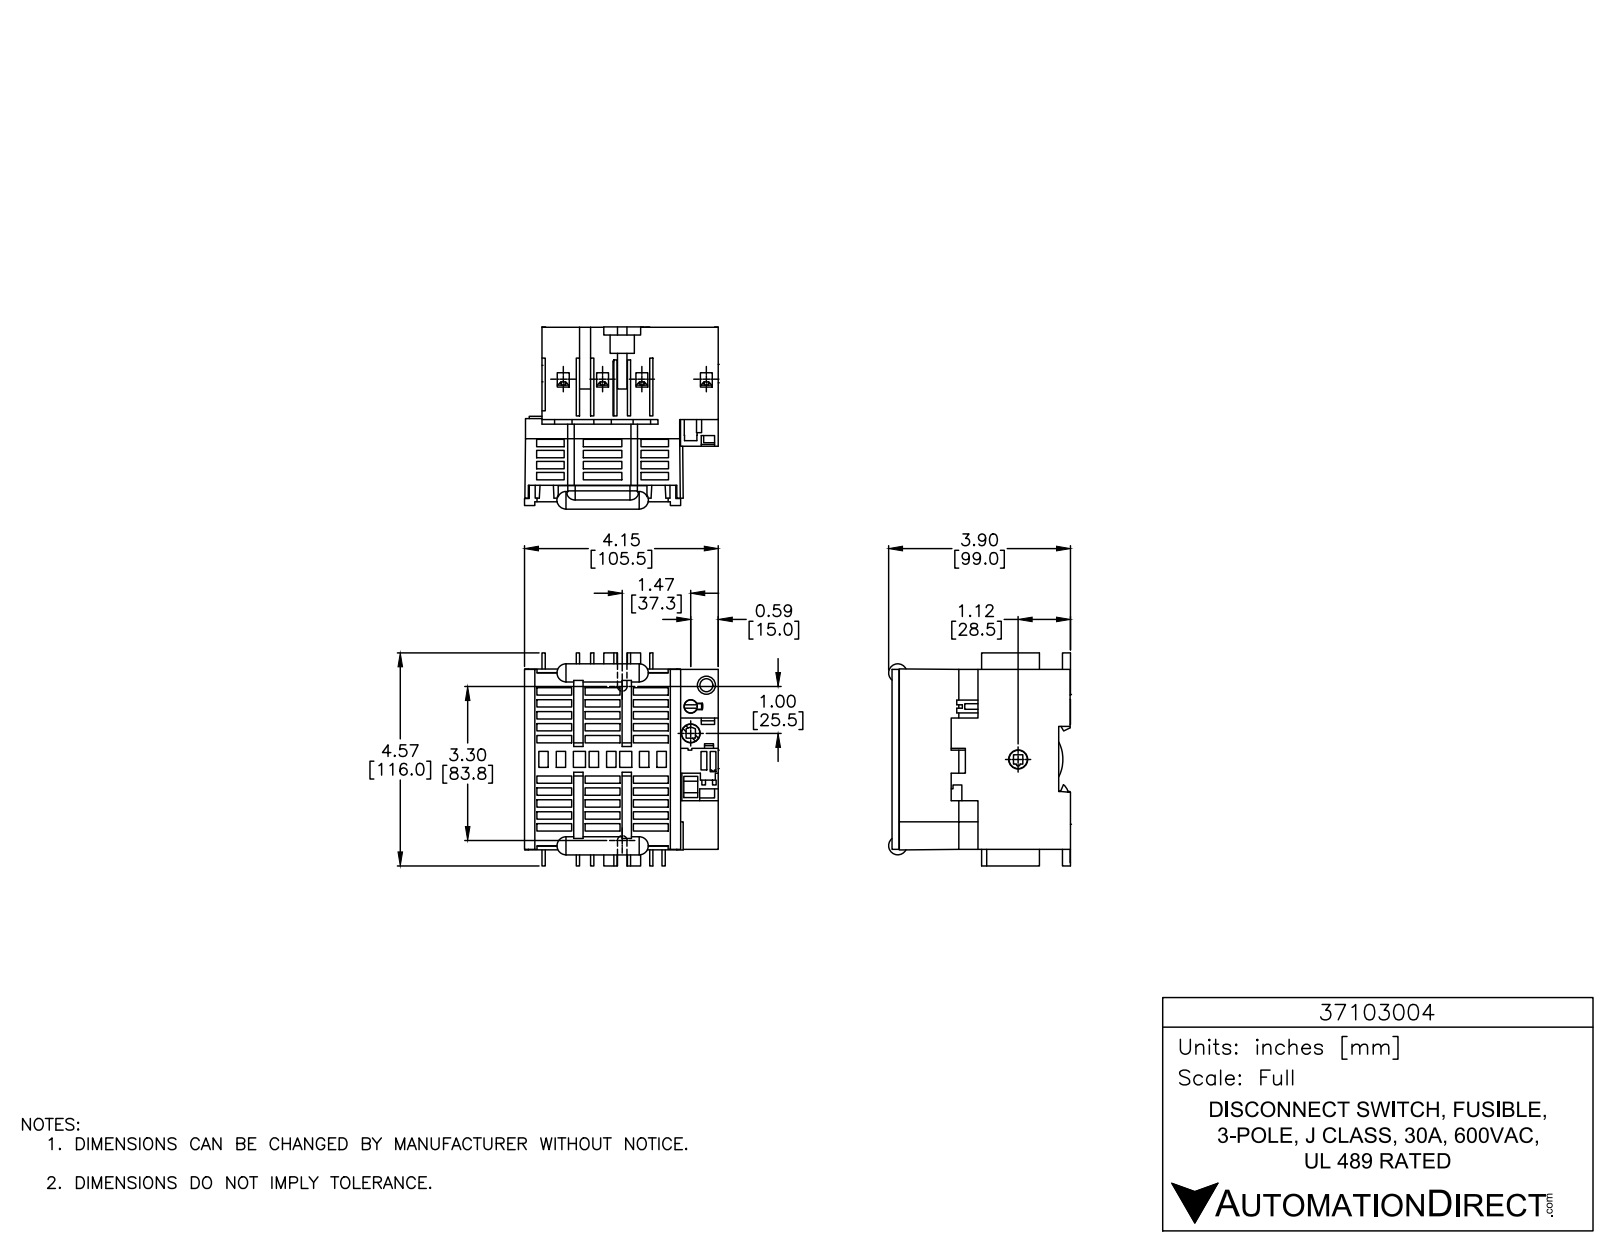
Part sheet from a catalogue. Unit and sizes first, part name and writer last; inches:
Units: inches
Overall size (bounding box): 4.567 × 4.154 × 3.906
Round holes (diameter × count): ⌀0.276 ×10, ⌀0.146 ×4, ⌀0.087 ×3, ⌀0.165 ×1, ⌀0.287 ×1, ⌀0.362 ×1, ⌀0.386 ×1, ⌀0.402 ×1, ⌀0.409 ×1
Round bosses / shafts (diameter × count): ⌀0.374 ×4, ⌀0.394 ×2, ⌀0.354 ×1, ⌀0.276 ×1
Partial cylindrical surfaces — rounded edges, fillets, slot ends (radius × count): R0.02 ×27, R0.01 ×20, R0.039 ×12, R0.197 ×12, R0.276 ×12, R0.051 ×8, R0.059 ×8, R0.118 ×5
Main face-to-face distances: 0.071, 0.079, 3.78, 1.274, 2.387, 3.661, 3.858, 1.764, 3.74, 1.353
Hole centre spacings: 0.843, 0.428, 3.277, 3.287, 1.685, 3.177, 0.375, 0.793
Volume: 32.19 in³ · Surface area: 212.9 in²
Bodies: 3 solids, 2210 faces (1893 planar, 272 cylindrical, 45 other)
Part name (STEP PRODUCT): 37103004
STEP written by: SolidWorks 2015 (AUTOMOTIVE_DESIGN)
